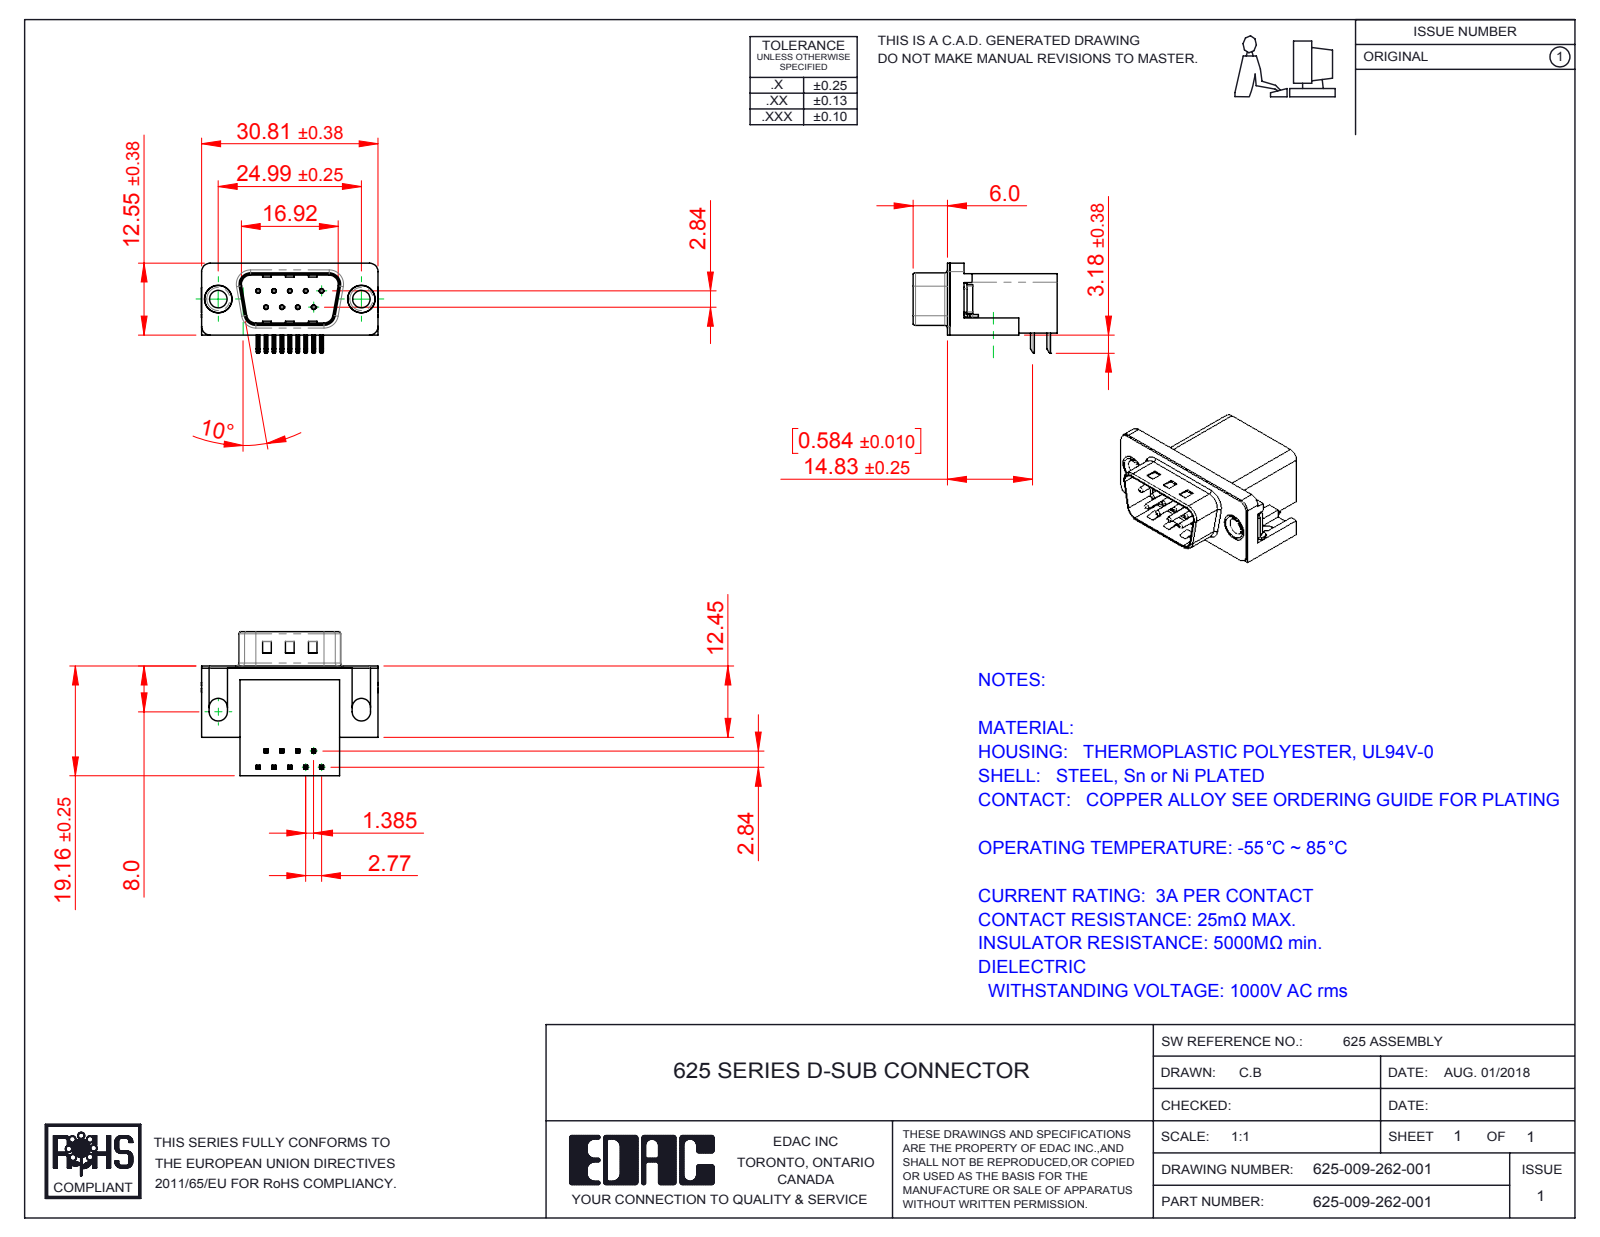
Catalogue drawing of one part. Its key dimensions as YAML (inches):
part_name: "625 Thru Hole Rivet; 625 Shell_9 Socket; 625 Housing_9 Socket; 625 Contact Top (+3 more)"
step_written_by: "SolidWorks 2016 (CONFIG_CONTROL_DESIGN)"
units: inches
bodies: {solids: 15, faces: 951, planar: 575, cylindrical: 295, other: 81}
overall_size: [1.216, 0.991, 0.619]
volume: 0.271
surface_area: 7.431
round_holes:
  - {diameter: 0.014, count: 9}
  - {diameter: 0.031, count: 9}
  - {diameter: 0.12, count: 2}
  - {diameter: 0.157, count: 2}
  - {diameter: 0.189, count: 2}
  - {diameter: 0.197, count: 2}
round_bosses_or_shafts:
  - {diameter: 0.03, count: 9}
  - {diameter: 0.193, count: 2}
  - {diameter: 0.187, count: 2}
  - {diameter: 0.152, count: 2}
partial_cylinders:
  - {radius: 0.01, count: 44}
  - {radius: 0.005, count: 18}
  - {radius: 0.039, count: 16}
  - {radius: 0.02, count: 9}
  - {radius: 0.059, count: 8}
  - {radius: 0.063, count: 8}
  - {radius: 0.035, count: 4}
  - {radius: 0.079, count: 4}
face_to_face_distances: [0.016, 0.407, 0.739, 0.754, 0.114, 0.64, 0.098, 0.014, 0.421, 0.264]
hole_center_spacings: [0.124, 0.109, 0.218, 0.198, 0.198, 0.327, 0.294, 0.295]
